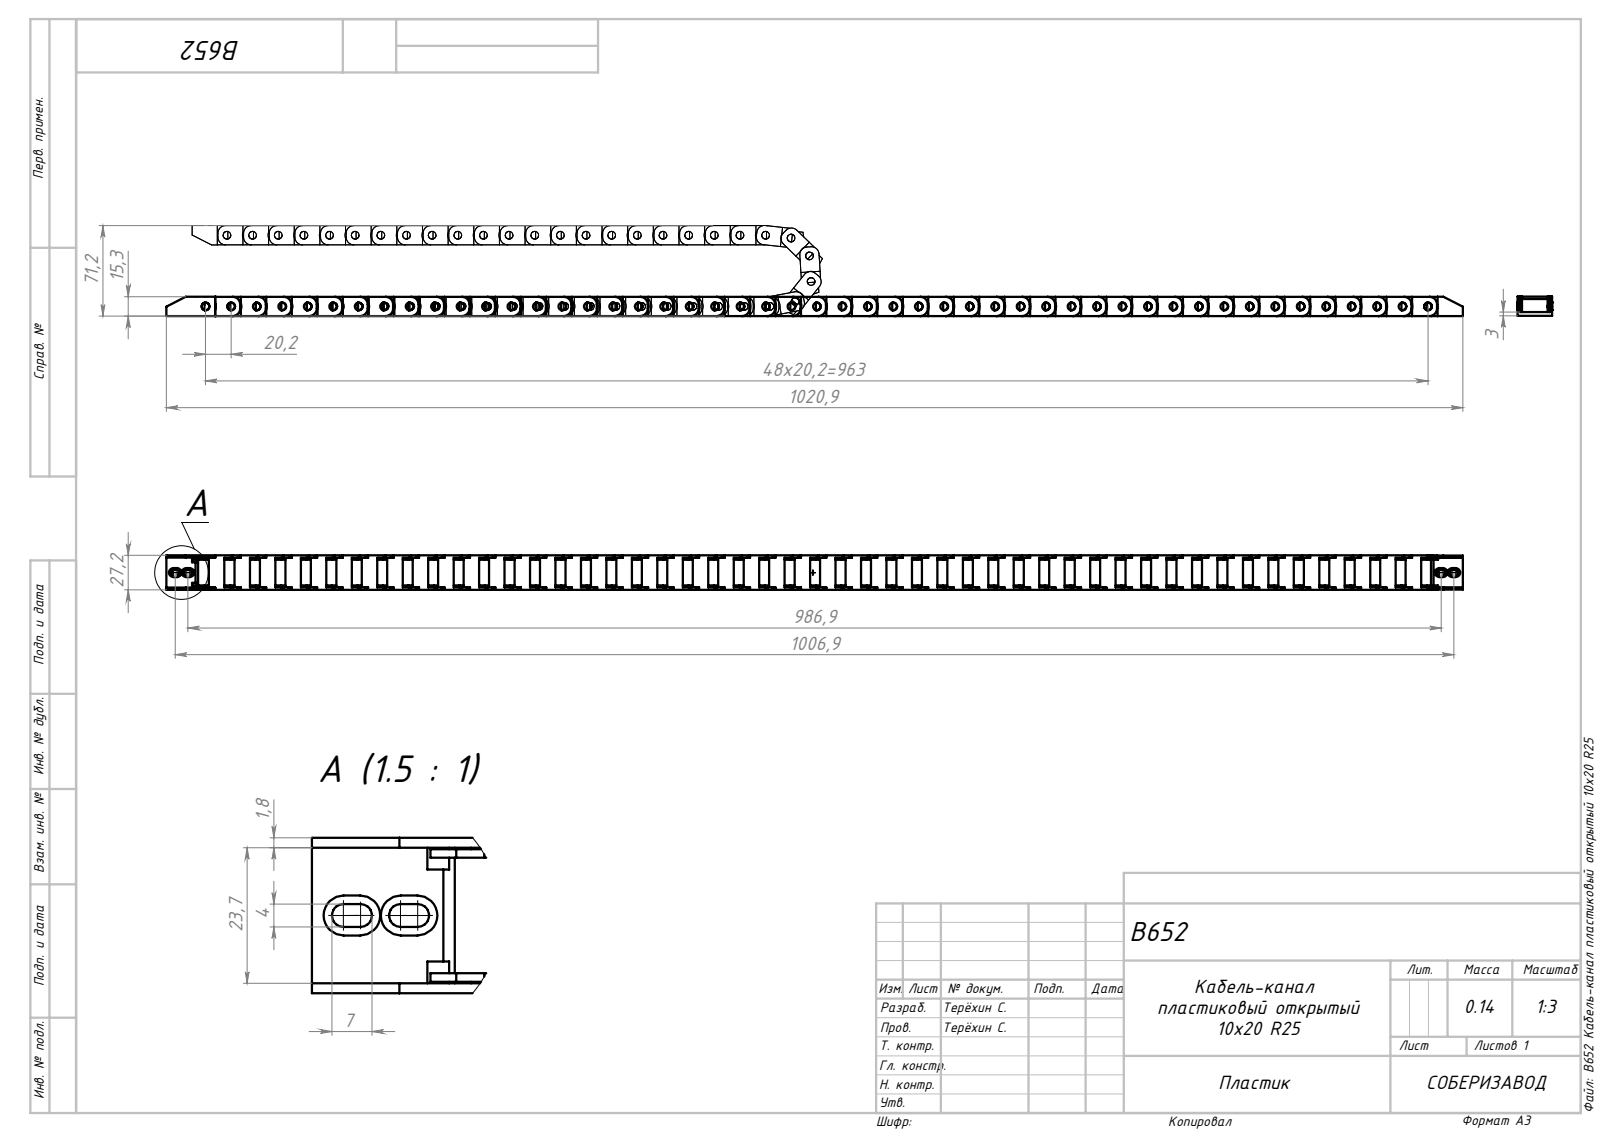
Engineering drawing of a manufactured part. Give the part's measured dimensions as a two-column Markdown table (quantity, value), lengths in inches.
| quantity | value |
| --- | --- |
| part name | B652 Кабель-канал пластиковый открытый 10x20 R25_00; B652 цепочка_00; B652 Крепление 2_00; Сборка4 (+1 more) |
| STEP written by | SolidWorks 2024 (AUTOMOTIVE_DESIGN) |
| units | inches |
| bodies | 50 solids, 2880 faces (1700 planar, 1172 cylindrical, 8 other) |
| overall size | 40.195 × 1.073 × 0.602 |
| volume | 8.195 in³ |
| surface area | 266.2 in² |
| round holes (diameter × count) | 0.24 × 49 |
| round bosses / shafts (diameter × count) | 0.236 × 49 |
| partial cylindrical surfaces (radius × count) | 0.118 × 192, 0.236 × 96, 0.217 × 49, 0.315 × 48, 0.079 × 8 |
| main face-to-face distances | 0.079, 0.992, 0.933, 0.059, 0.138, 0.854, 0.913, 0.596, 1.071, 0.795 |
| hole center spacings | 0.789, 1.579, 2.368, 3.157, 3.947, 4.736, 5.526, 6.315 |
